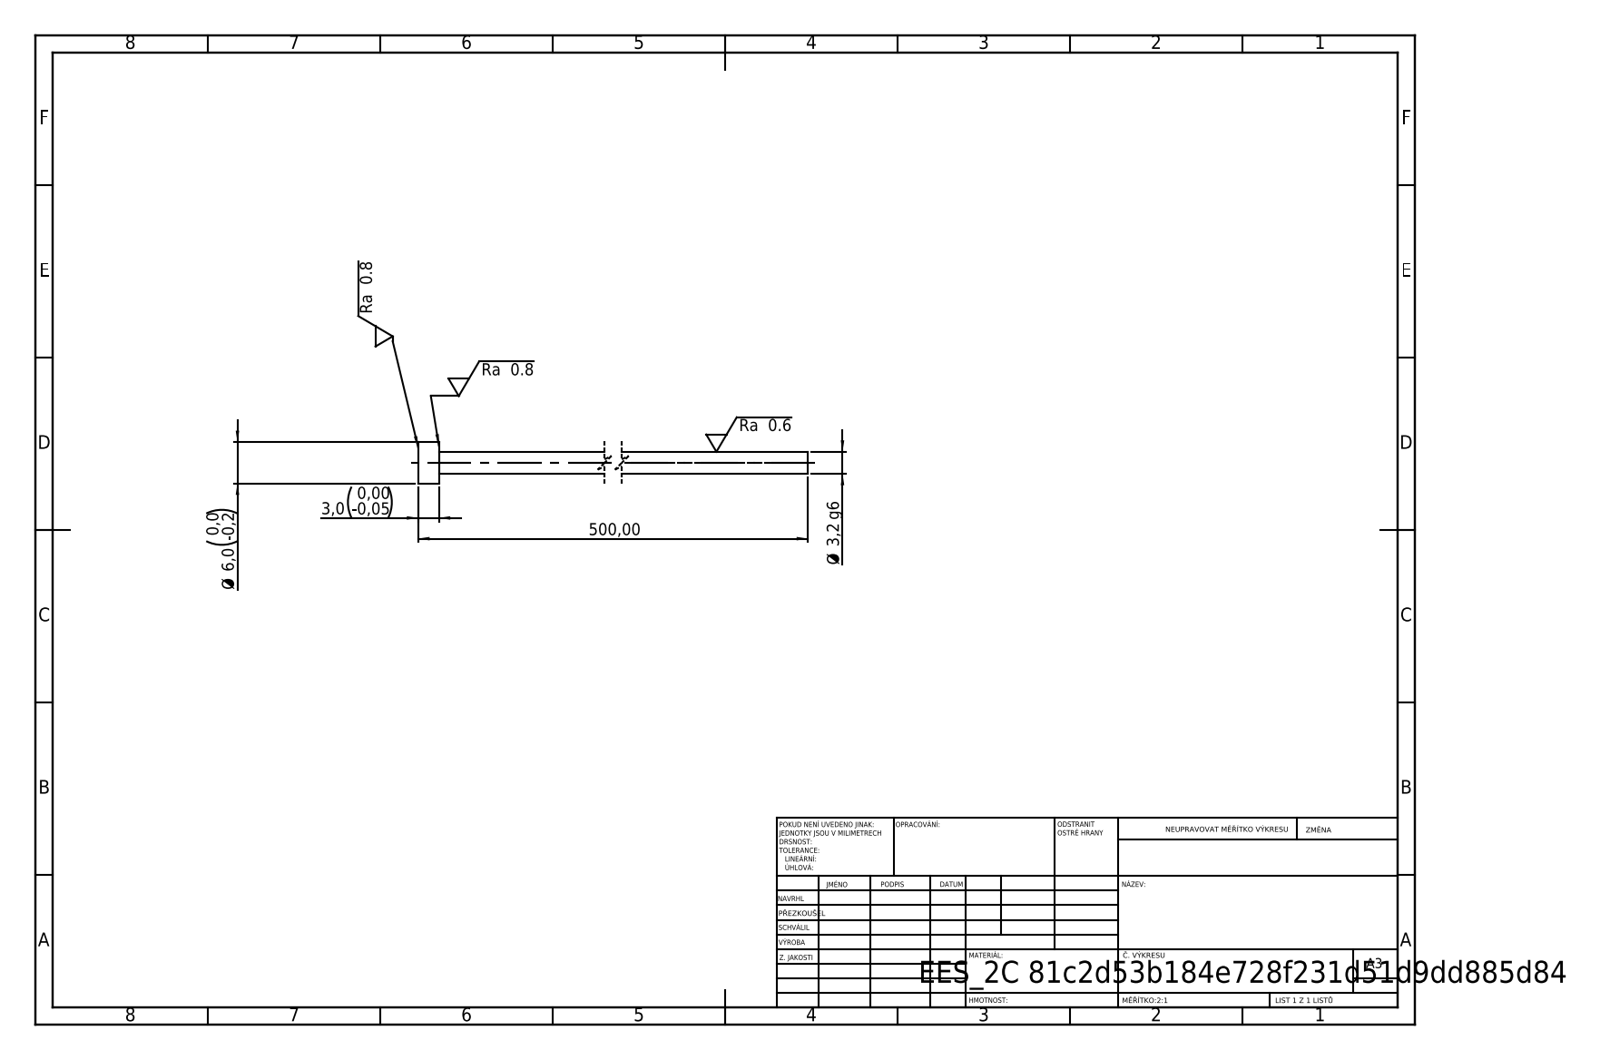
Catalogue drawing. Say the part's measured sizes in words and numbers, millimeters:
Its 3-D file was written by "SolidWorks 2019 (CONFIG_CONTROL_DESIGN)". It is 1 solid with 7 faces: 3 planar, 4 cylindrical and 0 other. Overall it measures 500 by 6 by 6 millimeters. Its volume is 4 082 cubic millimeters and its surface area 5 109 square millimeters. Round bosses or shafts: 1 of diameter 6, 1 of diameter 3.2. The main face-to-face distances are 3, 500, 497.
